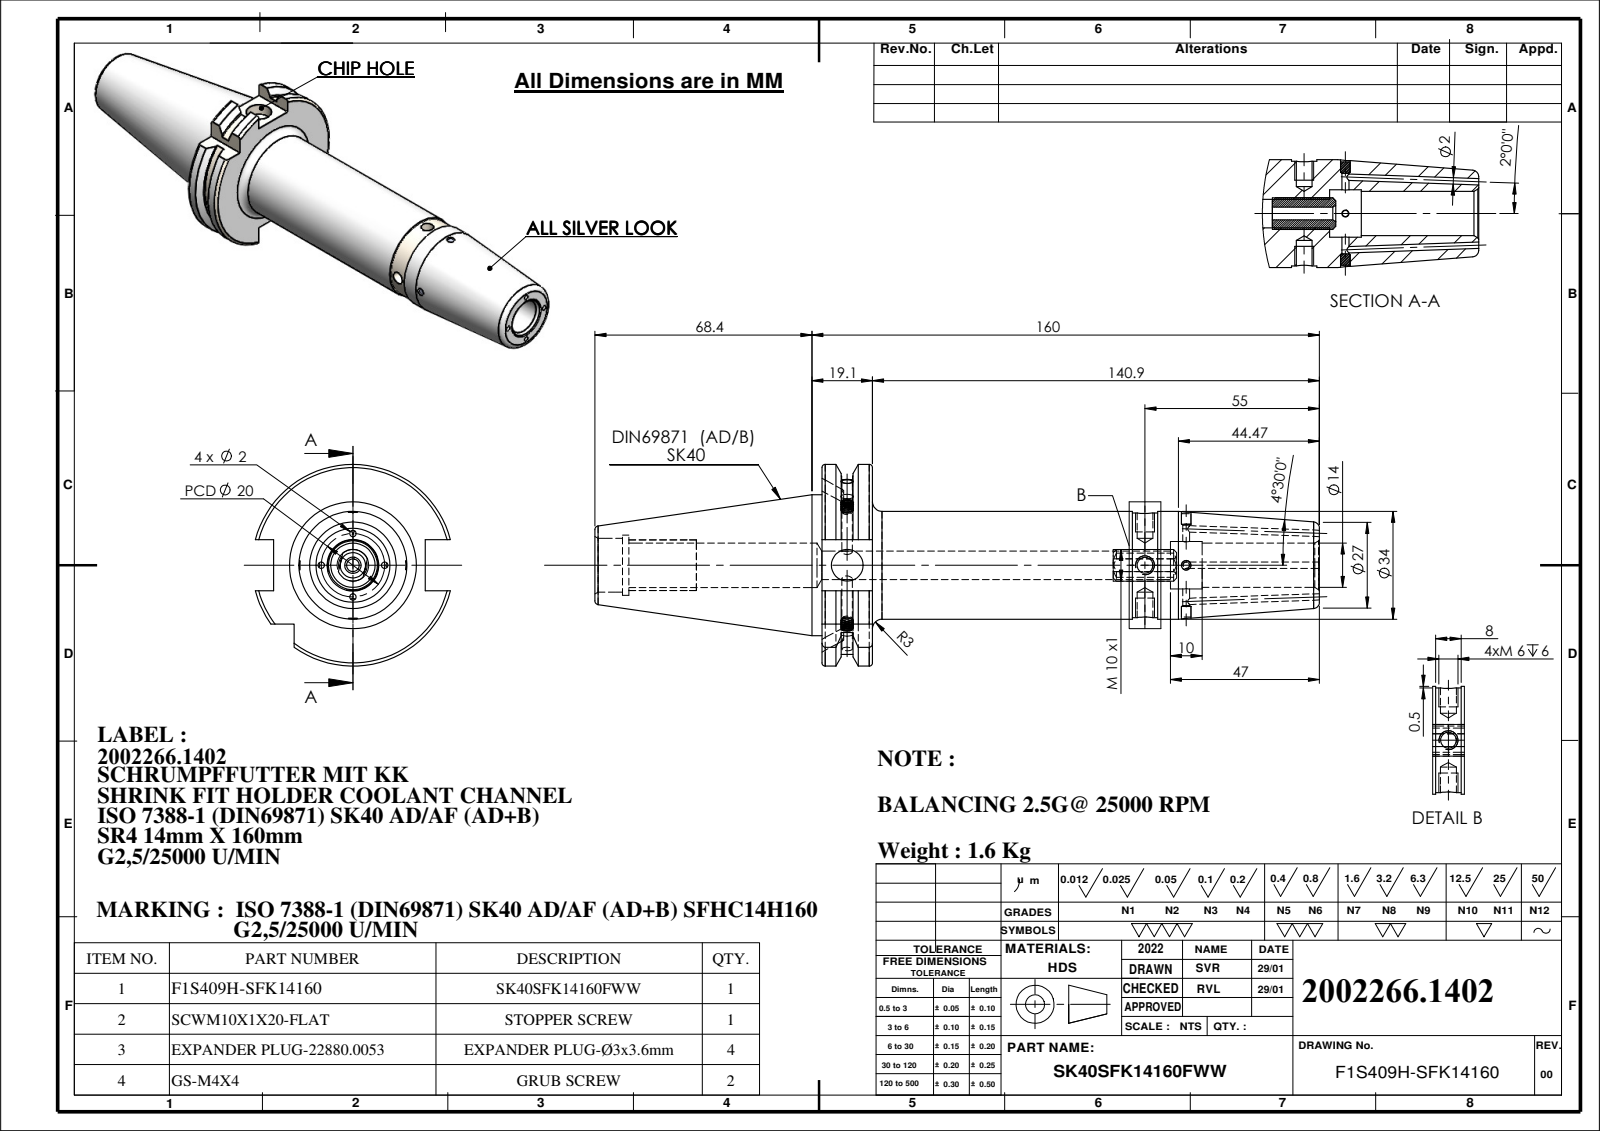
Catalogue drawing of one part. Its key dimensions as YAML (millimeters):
part_name: "SK40SFK14160FWW; GS-M4X4_DIN 913 - M4 x 4-N; EXPANDER PLUG Ø3x3.6; SCWM10X1X20-FLAT (+1 more)"
step_written_by: "SolidWorks 2018 (CONFIG_CONTROL_DESIGN)"
units: millimeters
bodies: {solids: 8, faces: 291, planar: 62, cylindrical: 103, other: 126}
overall_size: [228.4, 63.55, 61.48]
volume: 206171
surface_area: 43187
round_holes:
  - {diameter: 2, count: 4}
  - {diameter: 2.2, count: 2}
  - {diameter: 3, count: 2}
  - {diameter: 5, count: 2}
  - {diameter: 3.3, count: 1}
  - {diameter: 4, count: 1}
  - {diameter: 9, count: 1}
  - {diameter: 10, count: 1}
  - {diameter: 13.99, count: 1}
  - {diameter: 14, count: 1}
  - {diameter: 14.99, count: 1}
  - {diameter: 17, count: 1}
round_bosses_or_shafts:
  - {diameter: 4, count: 2}
  - {diameter: 44.45, count: 1}
  - {diameter: 34, count: 1}
  - {diameter: 33, count: 1}
partial_cylinders:
  - {radius: 5, count: 1}
  - {radius: 28.12, count: 1}
  - {radius: 31.77, count: 1}
face_to_face_distances: [15.9, 156.8, 140.9, 8, 16.1, 47.8, 71.6, 87.5, 228.4, 10.7]
hole_center_spacings: [13, 93.85, 106.85]
